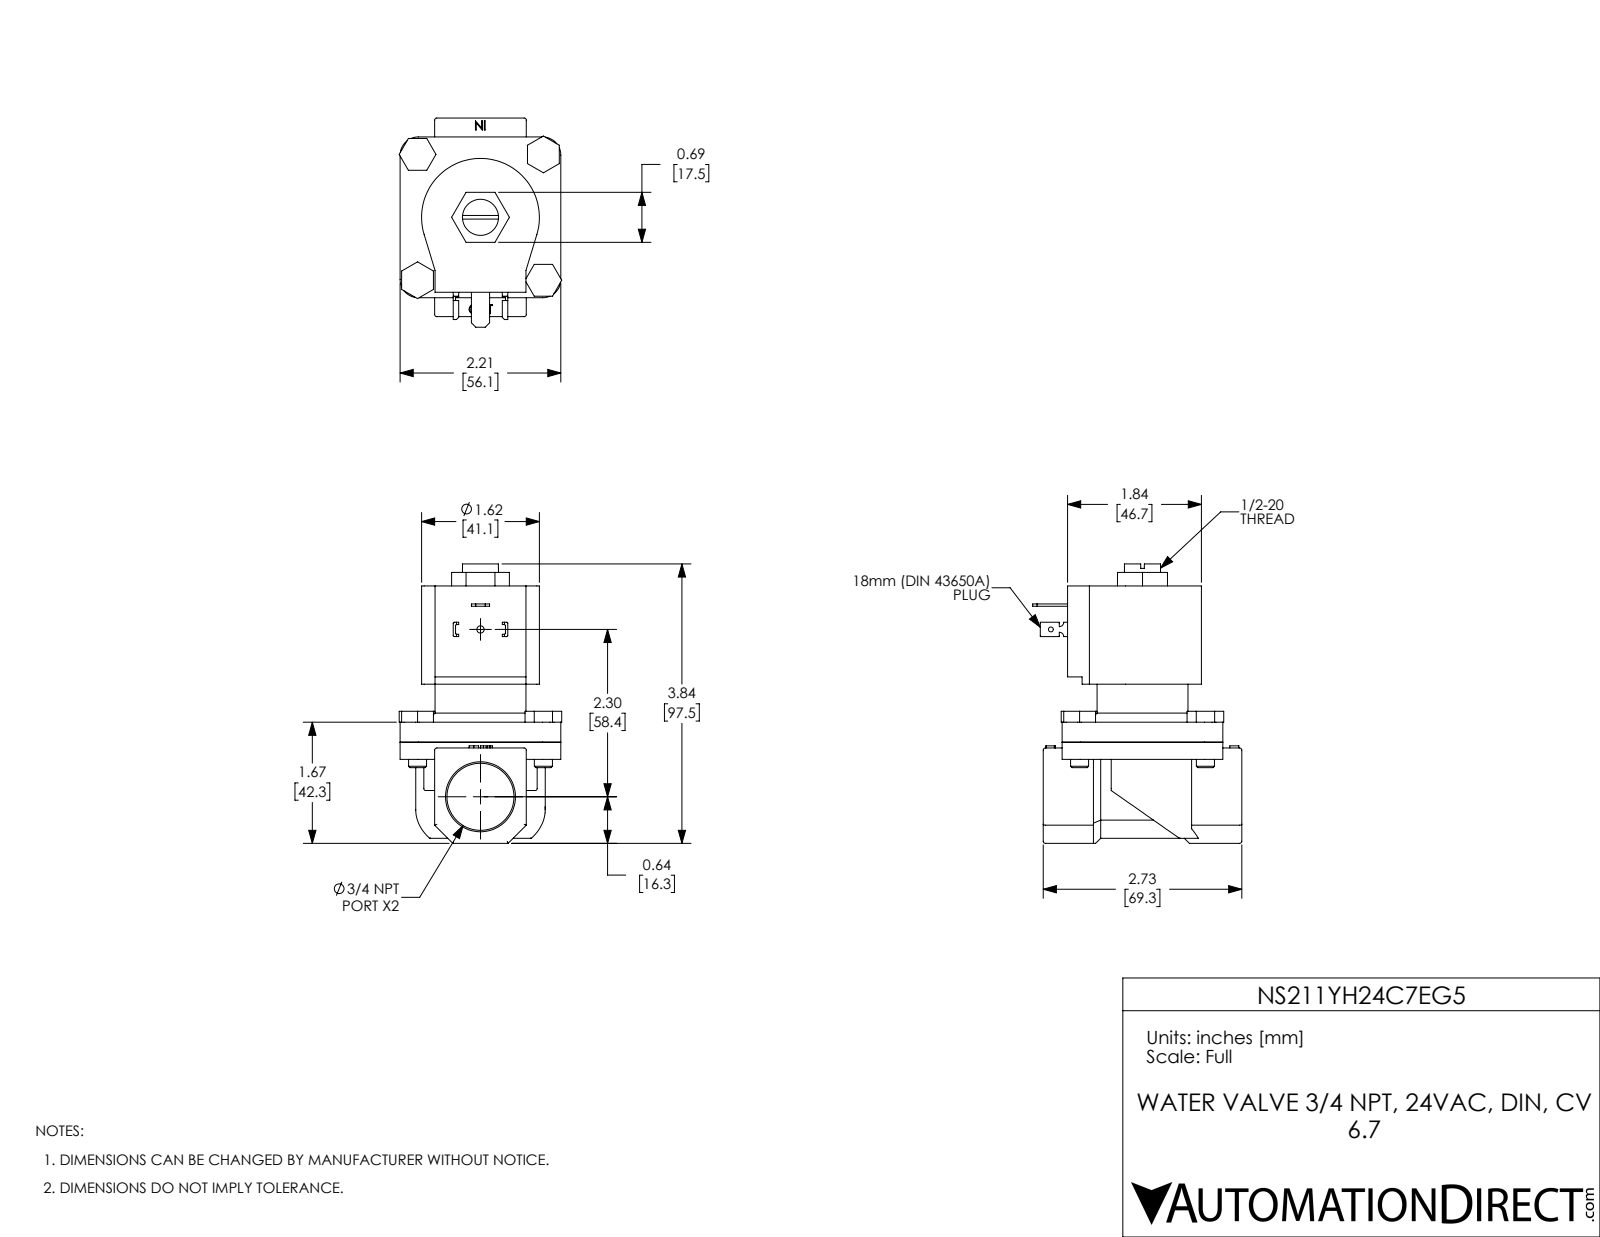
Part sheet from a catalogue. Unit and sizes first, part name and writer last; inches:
Units: inches
Overall size (bounding box): 3.84 × 2.875 × 2.235
Round holes (diameter × count): ⌀0.25 ×4, ⌀0.067 ×1, ⌀0.1 ×1, ⌀0.496 ×1, ⌀0.512 ×1, ⌀0.922 ×1, ⌀1.155 ×1
Round bosses / shafts (diameter × count): ⌀0.248 ×4, ⌀1.25 ×1
Partial cylindrical surfaces — rounded edges, fillets, slot ends (radius × count): R0.03 ×15, R0.015 ×8, R0.25 ×4, R0.06 ×2, R0.81 ×1, R0.89 ×1
Main face-to-face distances: 0.275, 2.148, 1.873, 0.475, 1.735, 2.21, 0.798, 0.523, 1.35, 0.236
Hole centre spacings: 1.223, 1.73, 2.446, 2.3
Volume: 9.853 in³ · Surface area: 64.15 in²
Bodies: 11 solids, 332 faces (198 planar, 99 cylindrical, 35 other)
Part name (STEP PRODUCT): NS211YH24C7EG5
STEP written by: SolidWorks 2024 (CONFIG_CONTROL_DESIGN)
